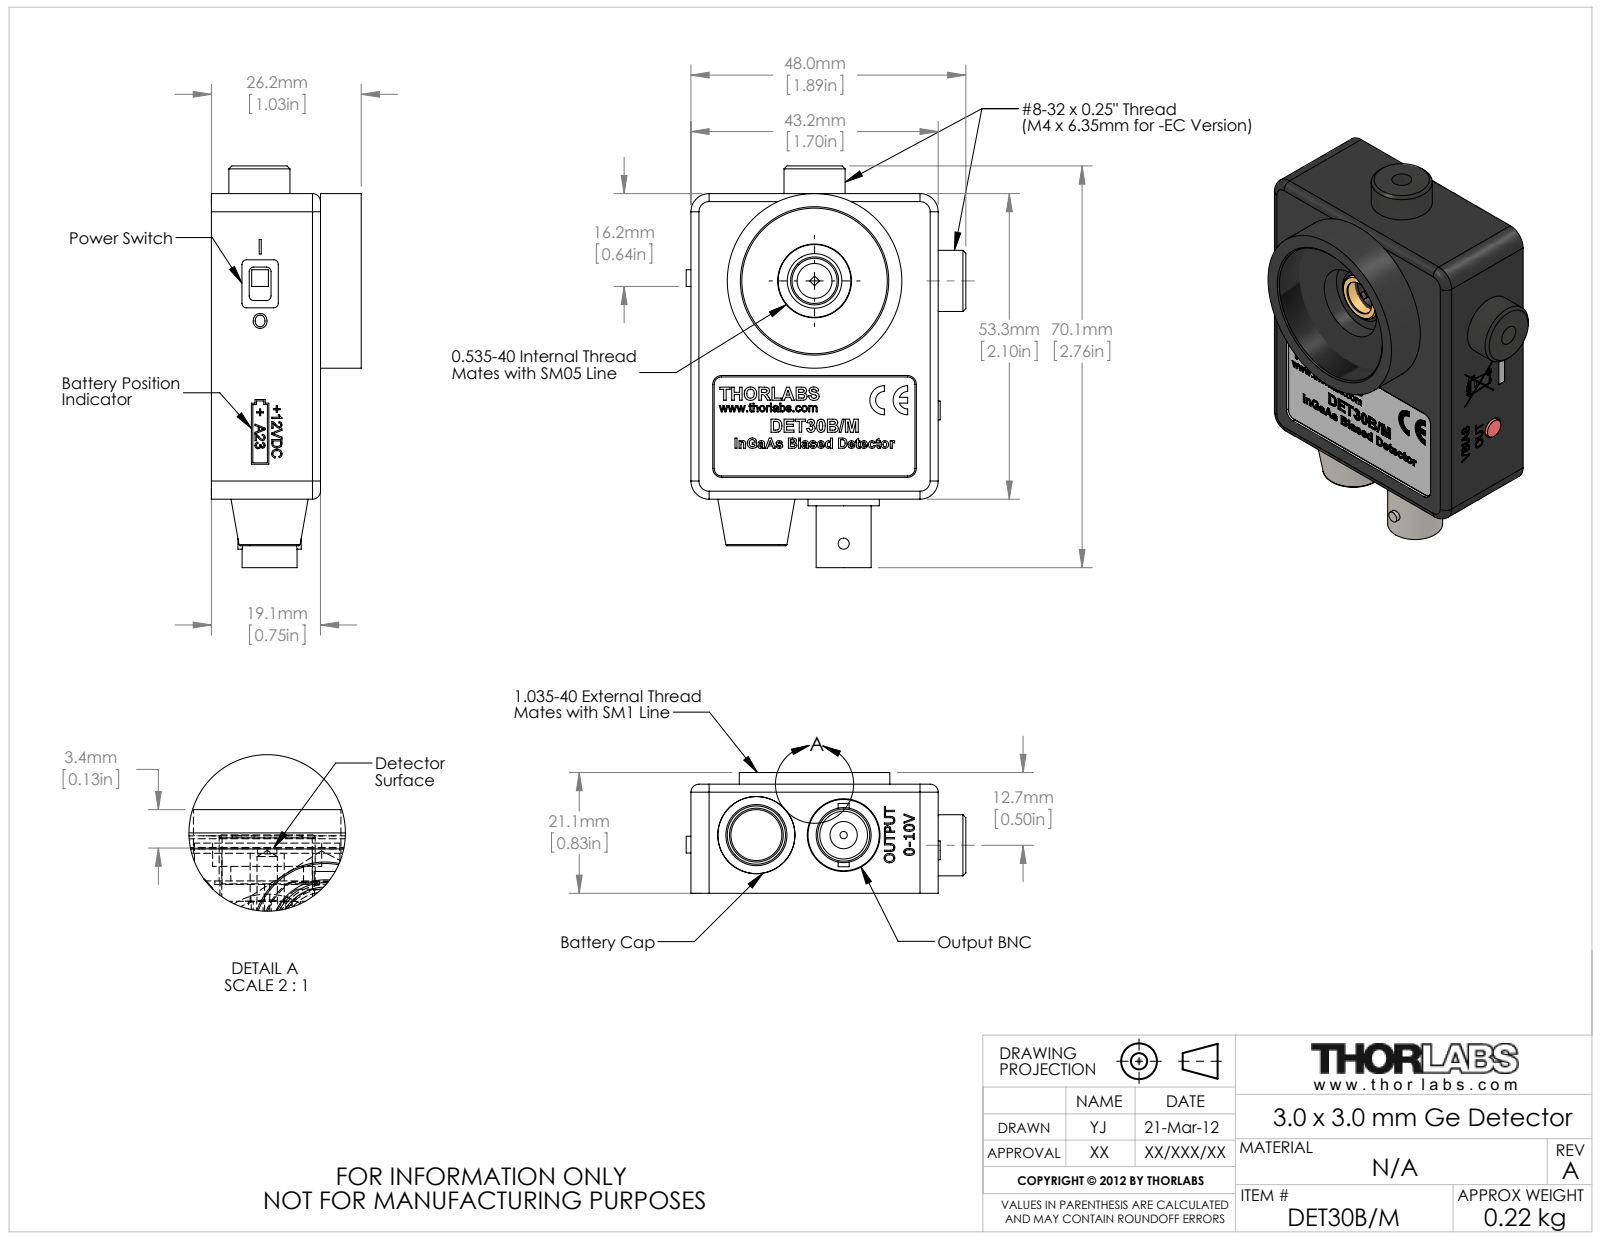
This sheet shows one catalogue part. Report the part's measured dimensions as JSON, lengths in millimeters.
{"part_name": "23160-E0W", "step_written_by": "SolidWorks 2011 (AUTOMOTIVE_DESIGN)", "units": "millimeters", "bodies": {"solids": 17, "faces": 1982, "planar": 1113, "cylindrical": 263, "other": 606}, "overall_size": [70.12, 48.83, 26.16], "volume_mm3": 20621, "surface_area_mm2": 23946, "round_holes": [[1.78, 7], [2.44, 4], [3.17, 4], [5.08, 4], [3.81, 3], [3.45, 2], [5.85, 2], [0.43, 1], [1.27, 1], [1.28, 1], [1.32, 1], [6.1, 1]], "round_bosses_or_shafts": [[3.73, 4], [2.18, 4], [1, 4], [10.67, 2], [5.99, 2], [0.45, 2], [30.48, 1], [26.29, 1]], "partial_cylinders_radius": [[3.17, 26], [0.79, 8], [2.41, 8], [0.1, 6], [0.5, 6], [0.4, 4], [1.27, 4], [1.4, 4]], "face_to_face_distances": [1.59, 2.54, 1.78, 1.27, 17.27, 15.68, 0.51, 18.54, 16.95, 19.05], "hole_center_spacings": [17.49, 20.01, 20.7, 22.43, 22.69, 27.08, 34.92, 38.19]}
